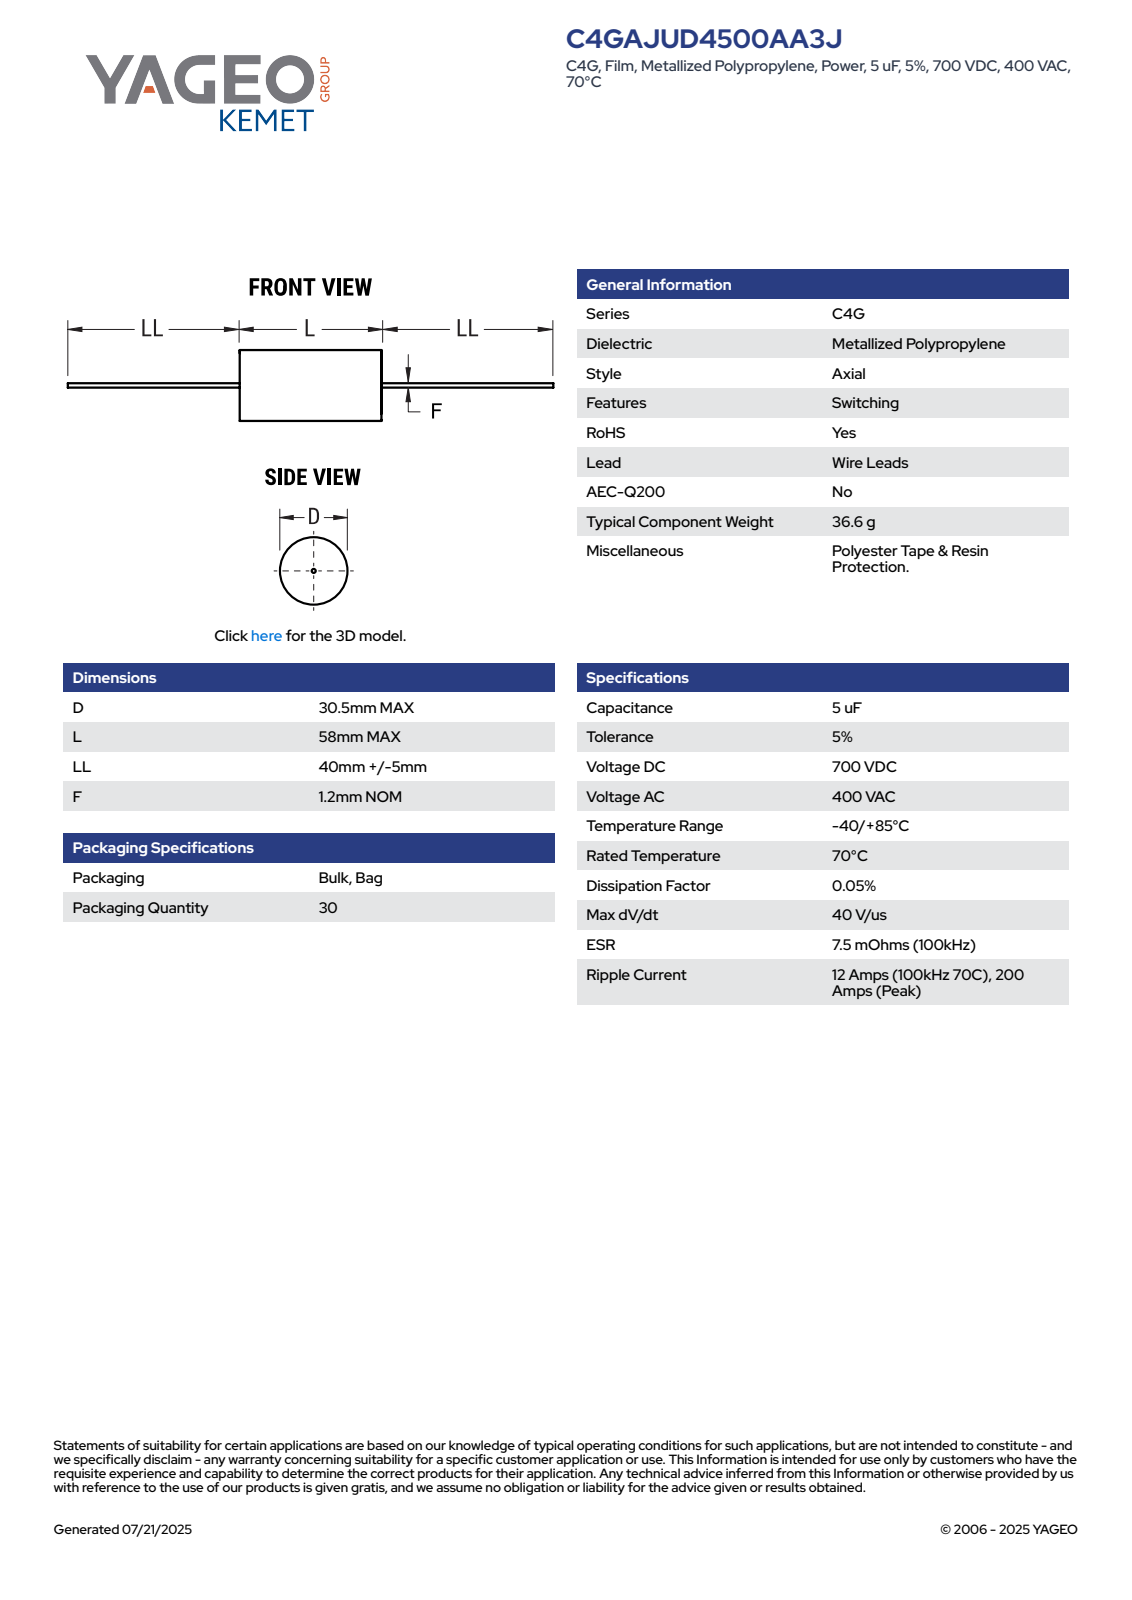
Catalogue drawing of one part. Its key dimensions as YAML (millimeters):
part_name: "CFP_ACWF_30.5X58_D30.5L58LL45F1.2"
step_written_by: "SolidWorks 2014 (AUTOMOTIVE_DESIGN)"
units: millimeters
bodies: {solids: 2, faces: 87, planar: 28, cylindrical: 28, other: 31}
overall_size: [148, 30.5, 30.5]
volume: 42477
surface_area: 8818
round_bosses_or_shafts:
  - {diameter: 30.5, count: 1}
  - {diameter: 1.2, count: 1}
partial_cylinders:
  - {radius: 15.24, count: 1}
face_to_face_distances: [58.01, 58, 45, 103, 44.99, 148, 103.01]
